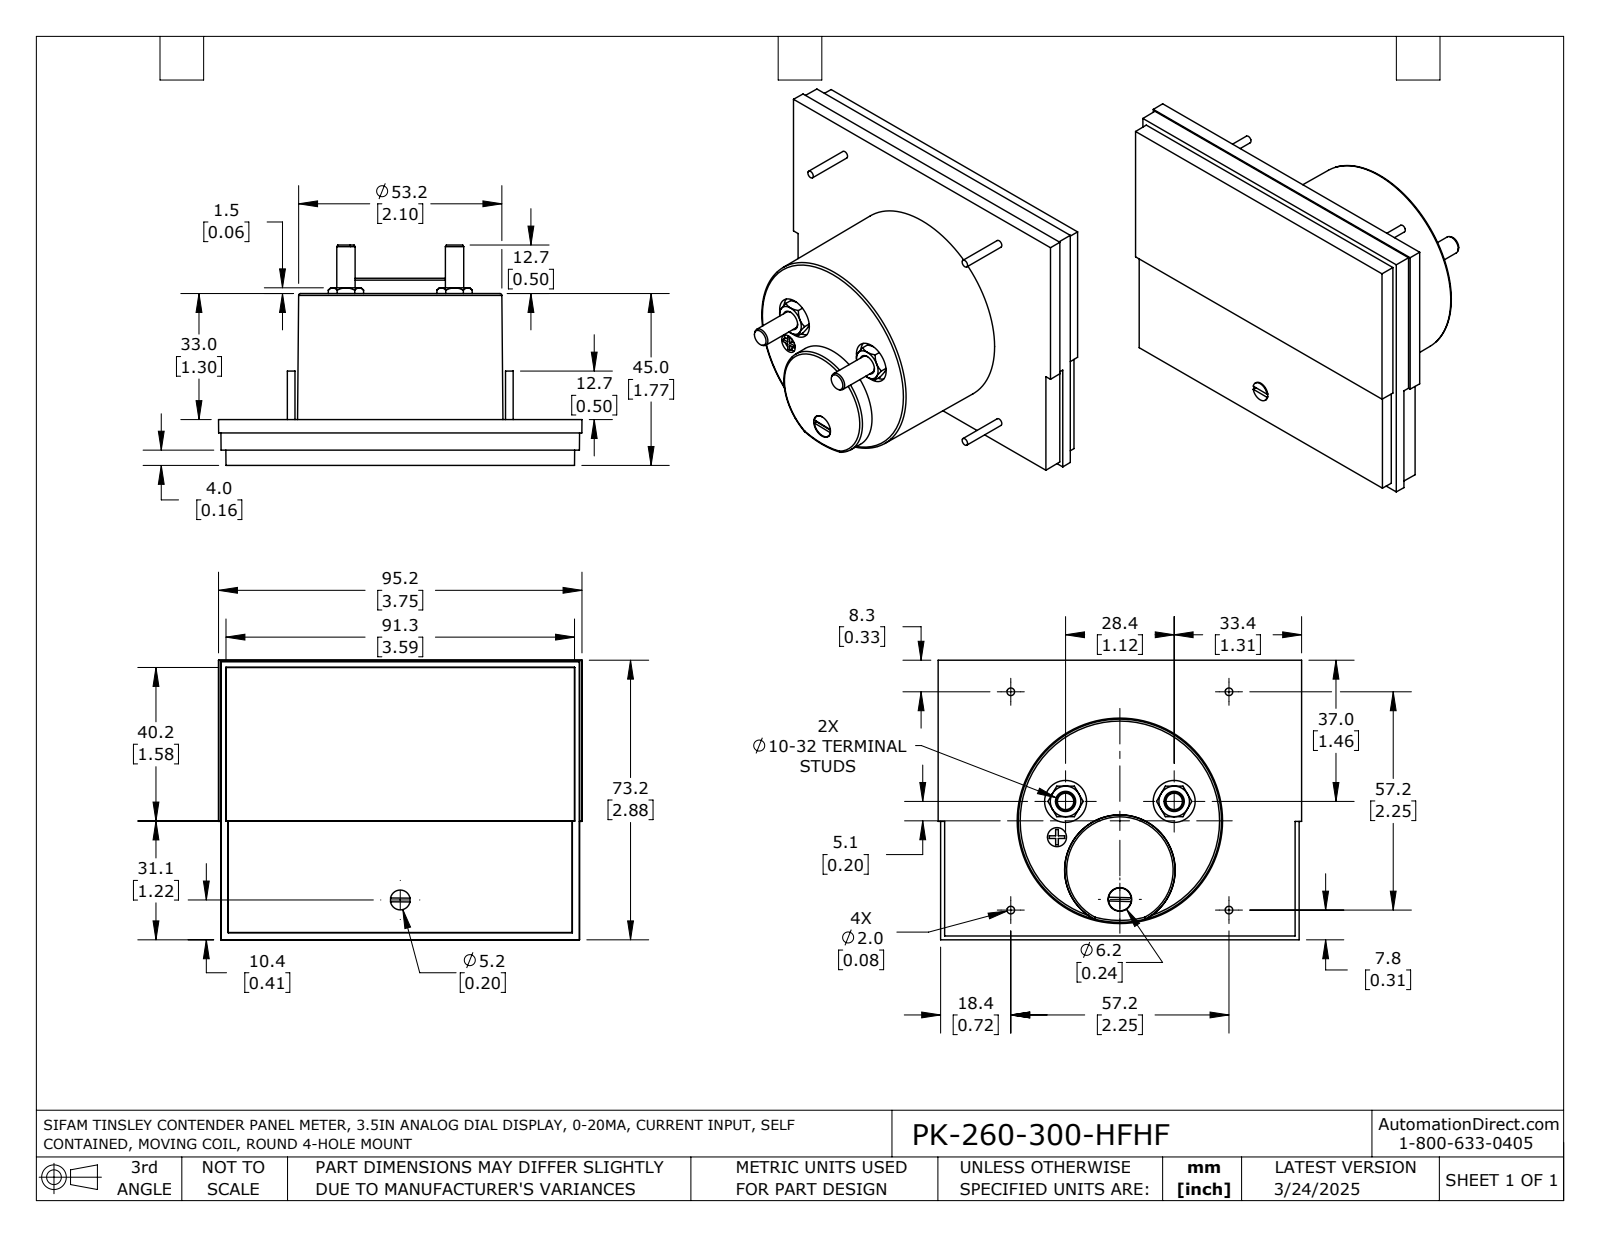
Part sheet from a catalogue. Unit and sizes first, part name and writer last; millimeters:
Units: millimetres
Overall size (bounding box): 95.2 × 73.2 × 57.7
Round holes (diameter × count): ⌀11 ×2, ⌀5 ×1, ⌀6.2 ×1
Round bosses / shafts (diameter × count): ⌀2 ×4, ⌀4.8 ×2, ⌀6 ×1, ⌀5.2 ×1
Partial cylindrical surfaces — rounded edges, fillets, slot ends (radius × count): R2.5 ×1
Main face-to-face distances: 12, 0.8, 11.3, 45, 33, 44.2, 4, 1.9, 8, 37
Hole centre spacings: 29.3, 9.6, 23.2, 28.4, 32.1
Volume: 154 800 mm³ · Surface area: 24 770 mm²
Bodies: 1 solid, 163 faces (76 planar, 31 cylindrical, 56 other)
Part name (STEP PRODUCT): PK-260-300-HFHF
STEP written by: SolidWorks 2021 (AUTOMOTIVE_DESIGN)
